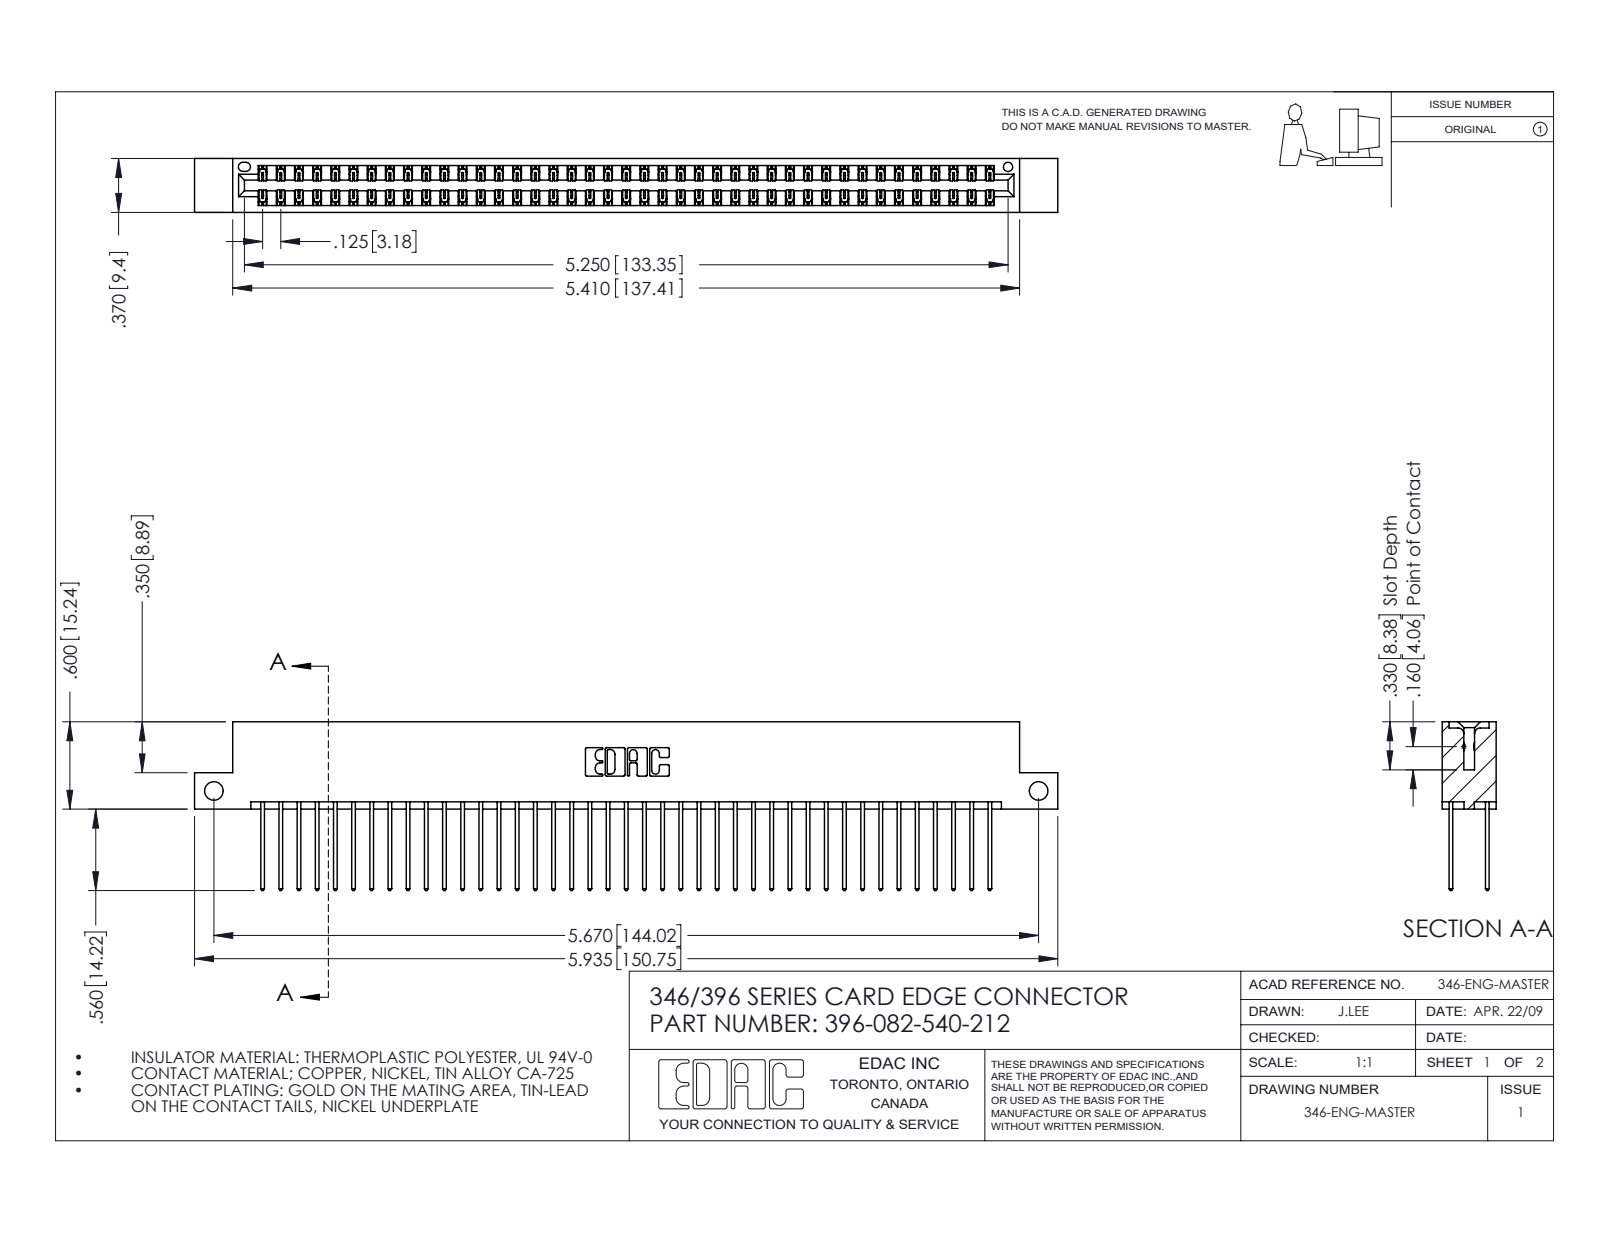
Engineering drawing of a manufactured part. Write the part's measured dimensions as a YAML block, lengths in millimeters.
part_name: "396-082-540-212; 345-292-001_345-293-140; 346 Part_Flush Mounting Lugs - Side Mount"
step_written_by: "SolidWorks 2016 (CONFIG_CONTROL_DESIGN)"
units: millimeters
bodies: {solids: 83, faces: 4386, planar: 2946, cylindrical: 1440, other: 0}
overall_size: [150.7, 29.5, 9.4]
volume: 14900
surface_area: 21820
round_holes:
  - {diameter: 3.3, count: 2}
  - {diameter: 1.6, count: 1}
partial_cylinders:
  - {radius: 0.2, count: 123}
  - {radius: 0.3, count: 82}
  - {radius: 0.3, count: 22}
  - {radius: 0.2, count: 6}
  - {radius: 0.8, count: 6}
  - {radius: 0.7, count: 3}
  - {radius: 0.4, count: 2}
  - {radius: 0.6, count: 2}
face_to_face_distances: [1.2, 8.2, 6.4, 1.8, 7.6, 0.6, 9.4, 7, 3.8, 5.6]
hole_center_spacings: [144]
